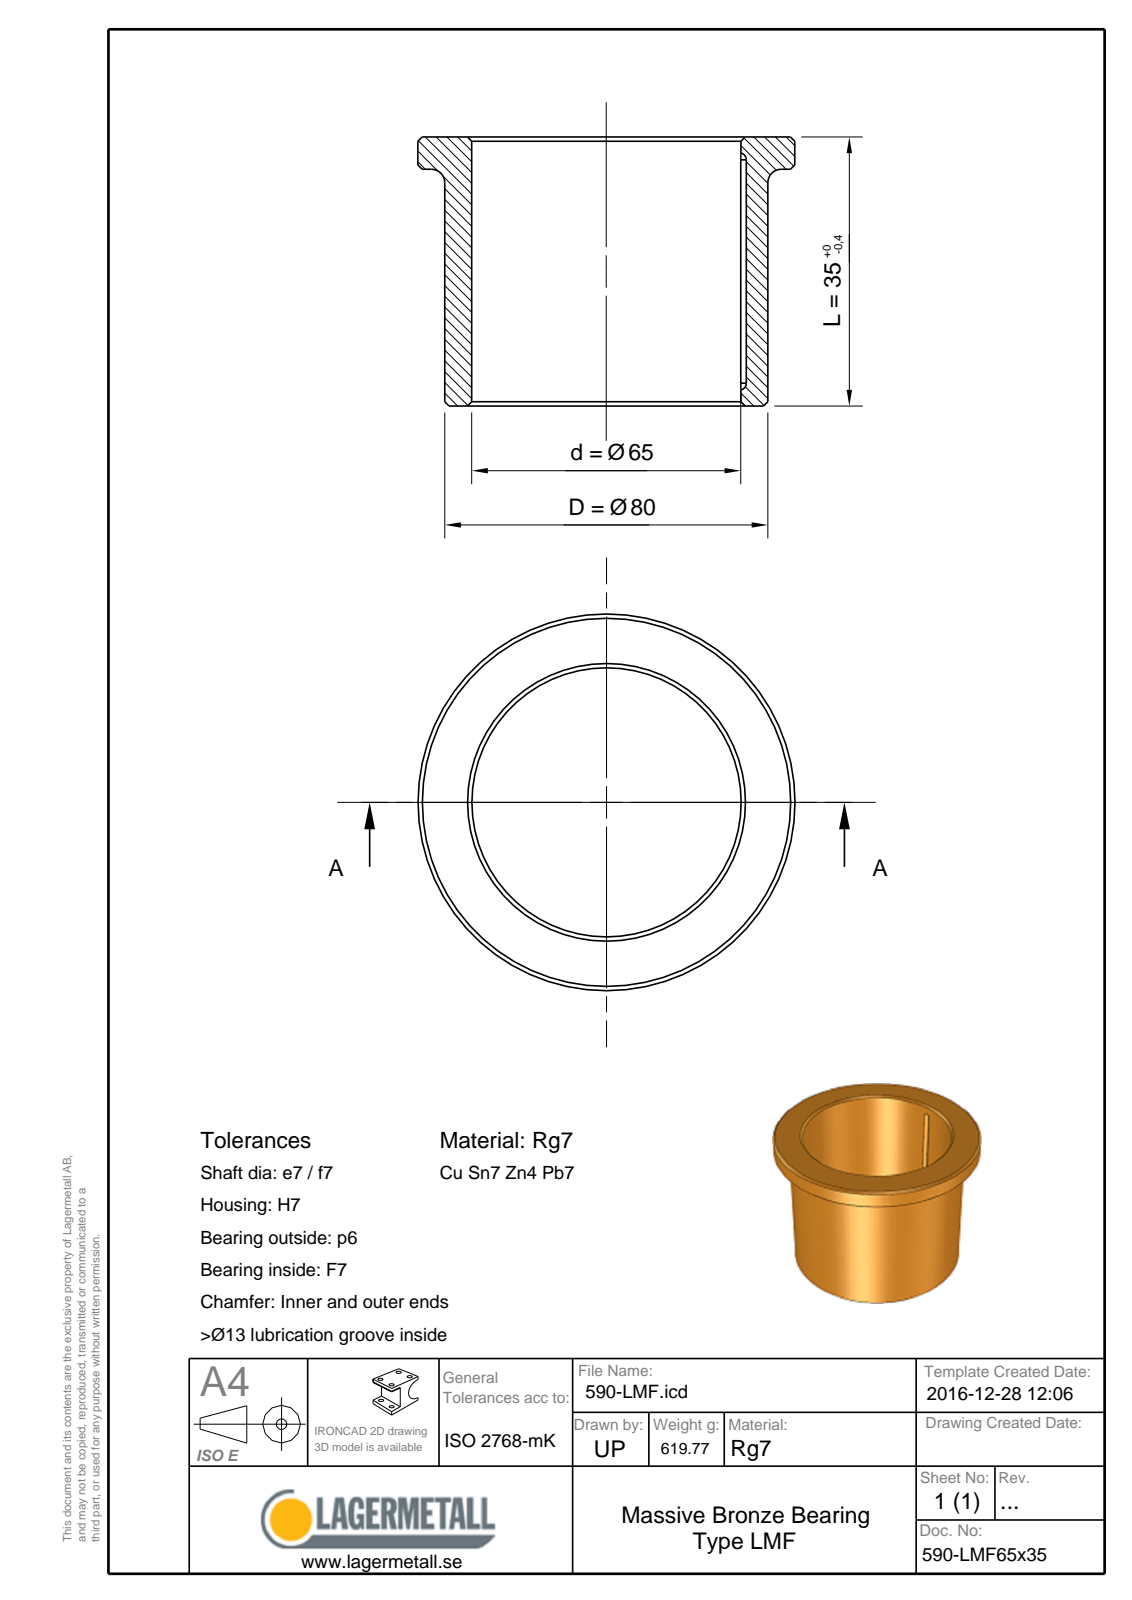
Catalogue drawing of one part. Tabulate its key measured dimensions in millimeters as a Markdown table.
| quantity | value |
| --- | --- |
| part name | 590-LMF65x35 |
| STEP written by | Spatial InterOp 3D (CONFIG_CONTROL_DESIGN) |
| units | millimeters |
| bodies | 1 solid, 17 faces (4 planar, 5 cylindrical, 8 other) |
| overall size | 90 × 90 × 35 |
| volume | 70 428 mm³ |
| surface area | 21 236 mm² |
| round holes (diameter × count) | 65 × 1 |
| round bosses / shafts (diameter × count) | 90 × 1, 80 × 1 |
| partial cylindrical surfaces (radius × count) | 1.75 × 2 |
| main face-to-face distances | 35, 27, 8 |
